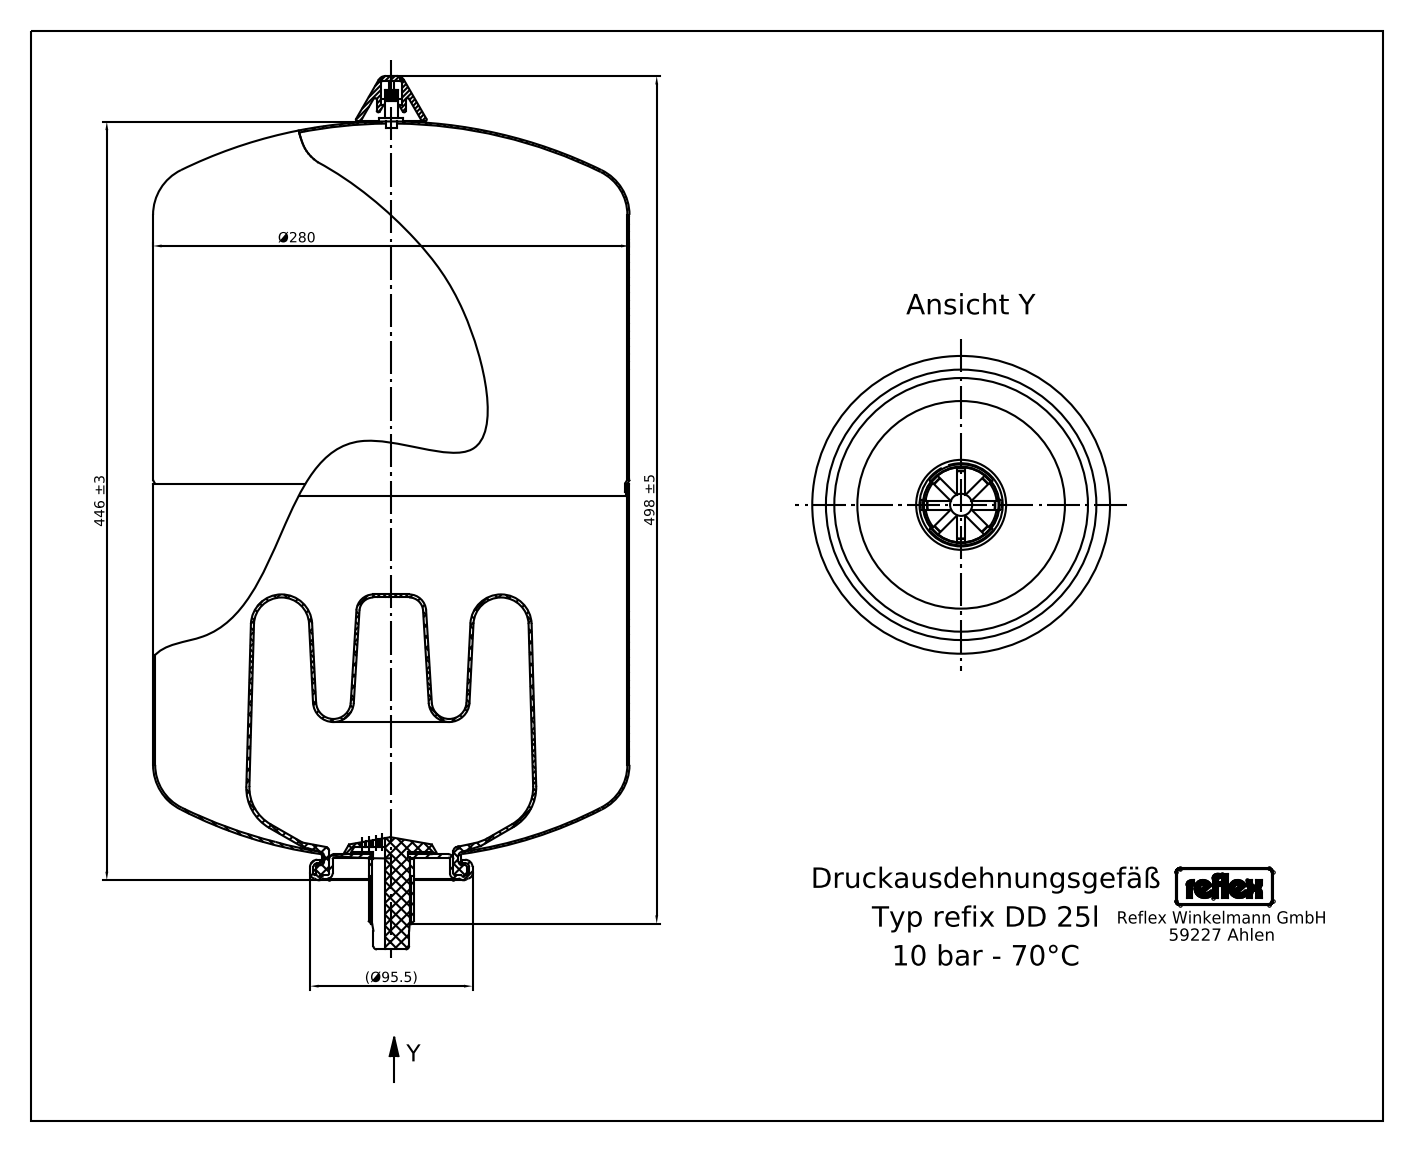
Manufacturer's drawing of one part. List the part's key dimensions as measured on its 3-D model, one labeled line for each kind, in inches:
STEP written by: Mechanical Desktop 2008 (CONFIG_CONTROL_DESIGN)
Units: inches
Bodies: 14 solids, 217 faces (129 planar, 46 cylindrical, 42 other)
Overall size (bounding box): 20.236 × 11.036 × 11.024
Volume: 1 498 in³ · Surface area: 1 143 in²
Round holes (diameter × count): ⌀0.555 ×1, ⌀0.744 ×1
Round bosses / shafts (diameter × count): ⌀11.024 ×1, ⌀3.78 ×1, ⌀3.228 ×1, ⌀1.059 ×1, ⌀0.673 ×1, ⌀0.354 ×1, ⌀0.236 ×1
Partial cylindrical surfaces — rounded edges, fillets, slot ends (radius × count): R0.044 ×4, R0.018 ×3, R0.03 ×2, R0.053 ×2, R0.073 ×2, R0.074 ×2, R0.1 ×2, R0.022 ×1
Main face-to-face distances: 12.795, 1.929, 14.724, 0.512, 2.441, 15.236, 0.059, 8.819, 8.307, 6.378
